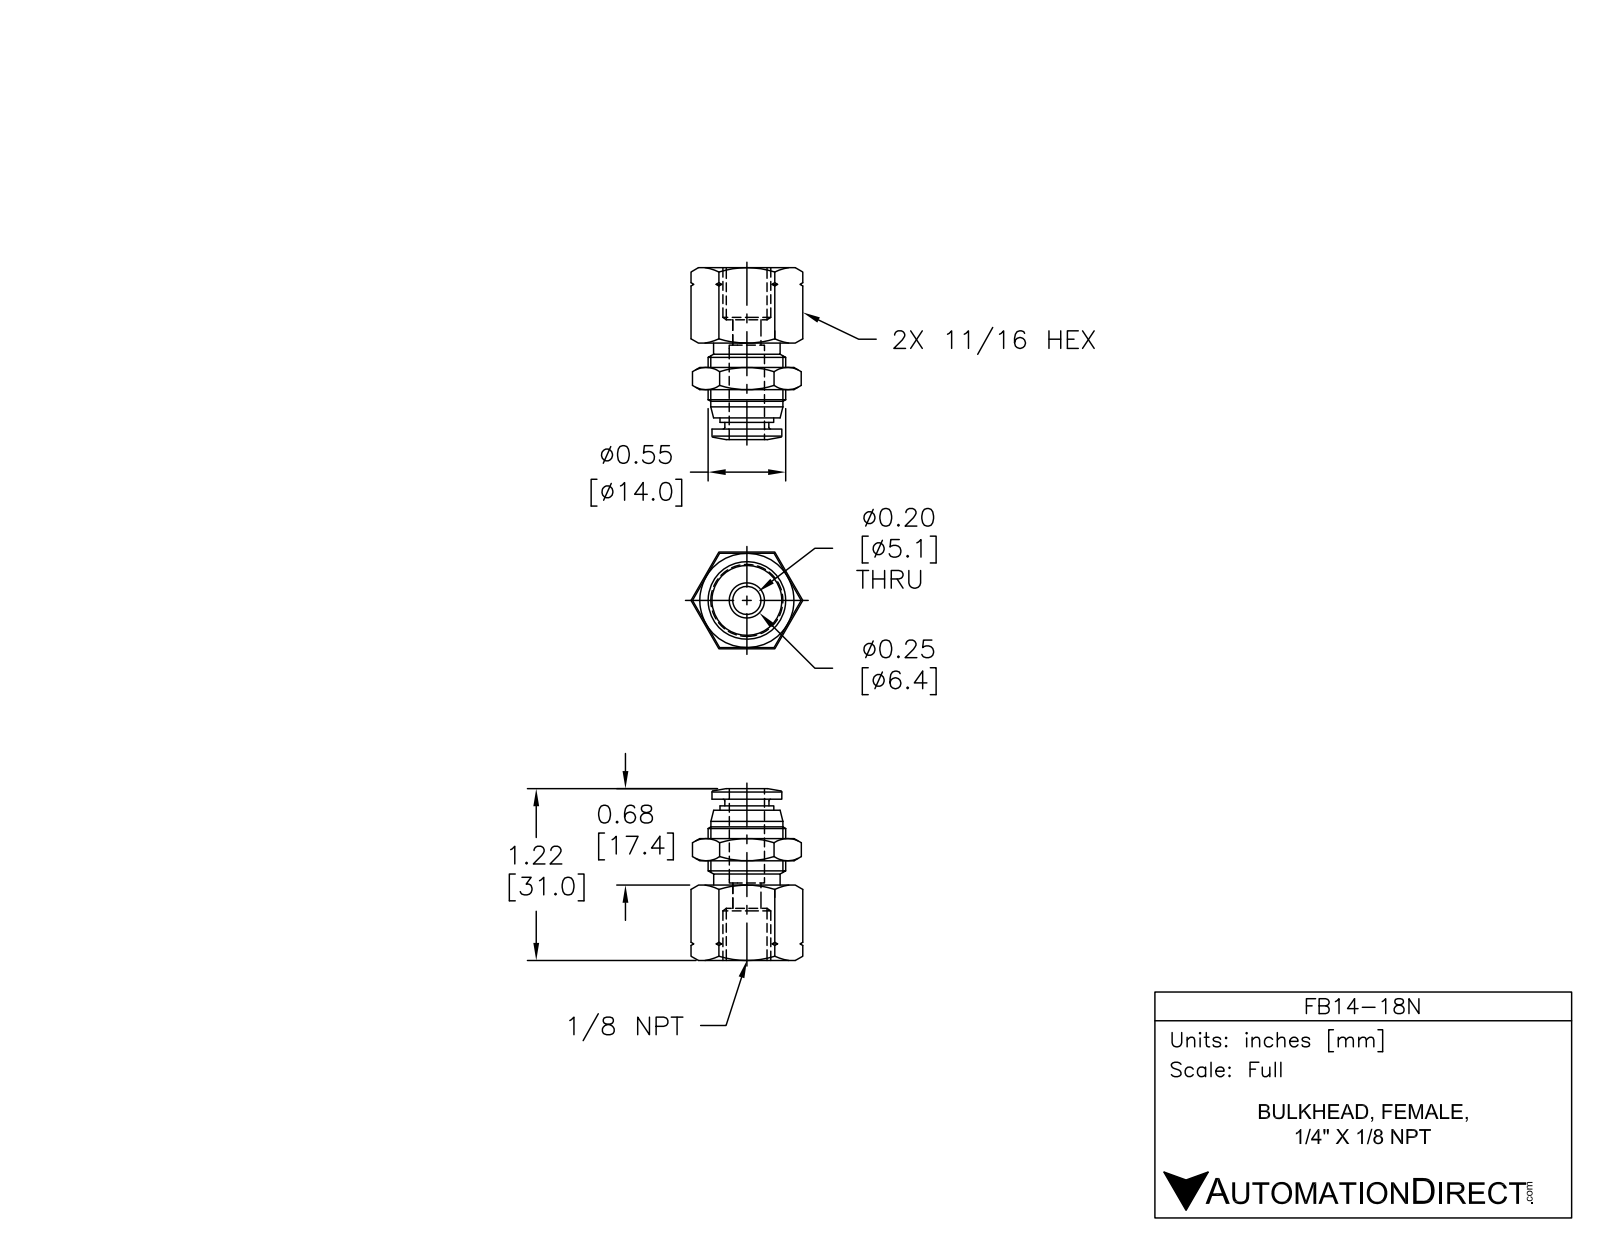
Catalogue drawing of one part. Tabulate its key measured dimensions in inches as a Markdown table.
| quantity | value |
| --- | --- |
| part name | FB14-18N |
| STEP written by | SolidWorks 2015 (AUTOMOTIVE_DESIGN) |
| units | inches |
| bodies | 1 solid, 93 faces (21 planar, 18 cylindrical, 54 other) |
| overall size | 1.22 × 0.794 × 0.687 |
| volume | 0.293 in³ |
| surface area | 4.786 in² |
| round holes (diameter × count) | 0.197 × 1, 0.258 × 1 |
| round bosses / shafts (diameter × count) | 0.551 × 1, 0.512 × 1, 0.496 × 1, 0.472 × 1, 0.382 × 1, 0.313 × 1 |
| main face-to-face distances | 0.687, 0.678, 0.535, 0.669, 0.856, 0.32, 0.698, 0.163, 0.157, 1.146 |
